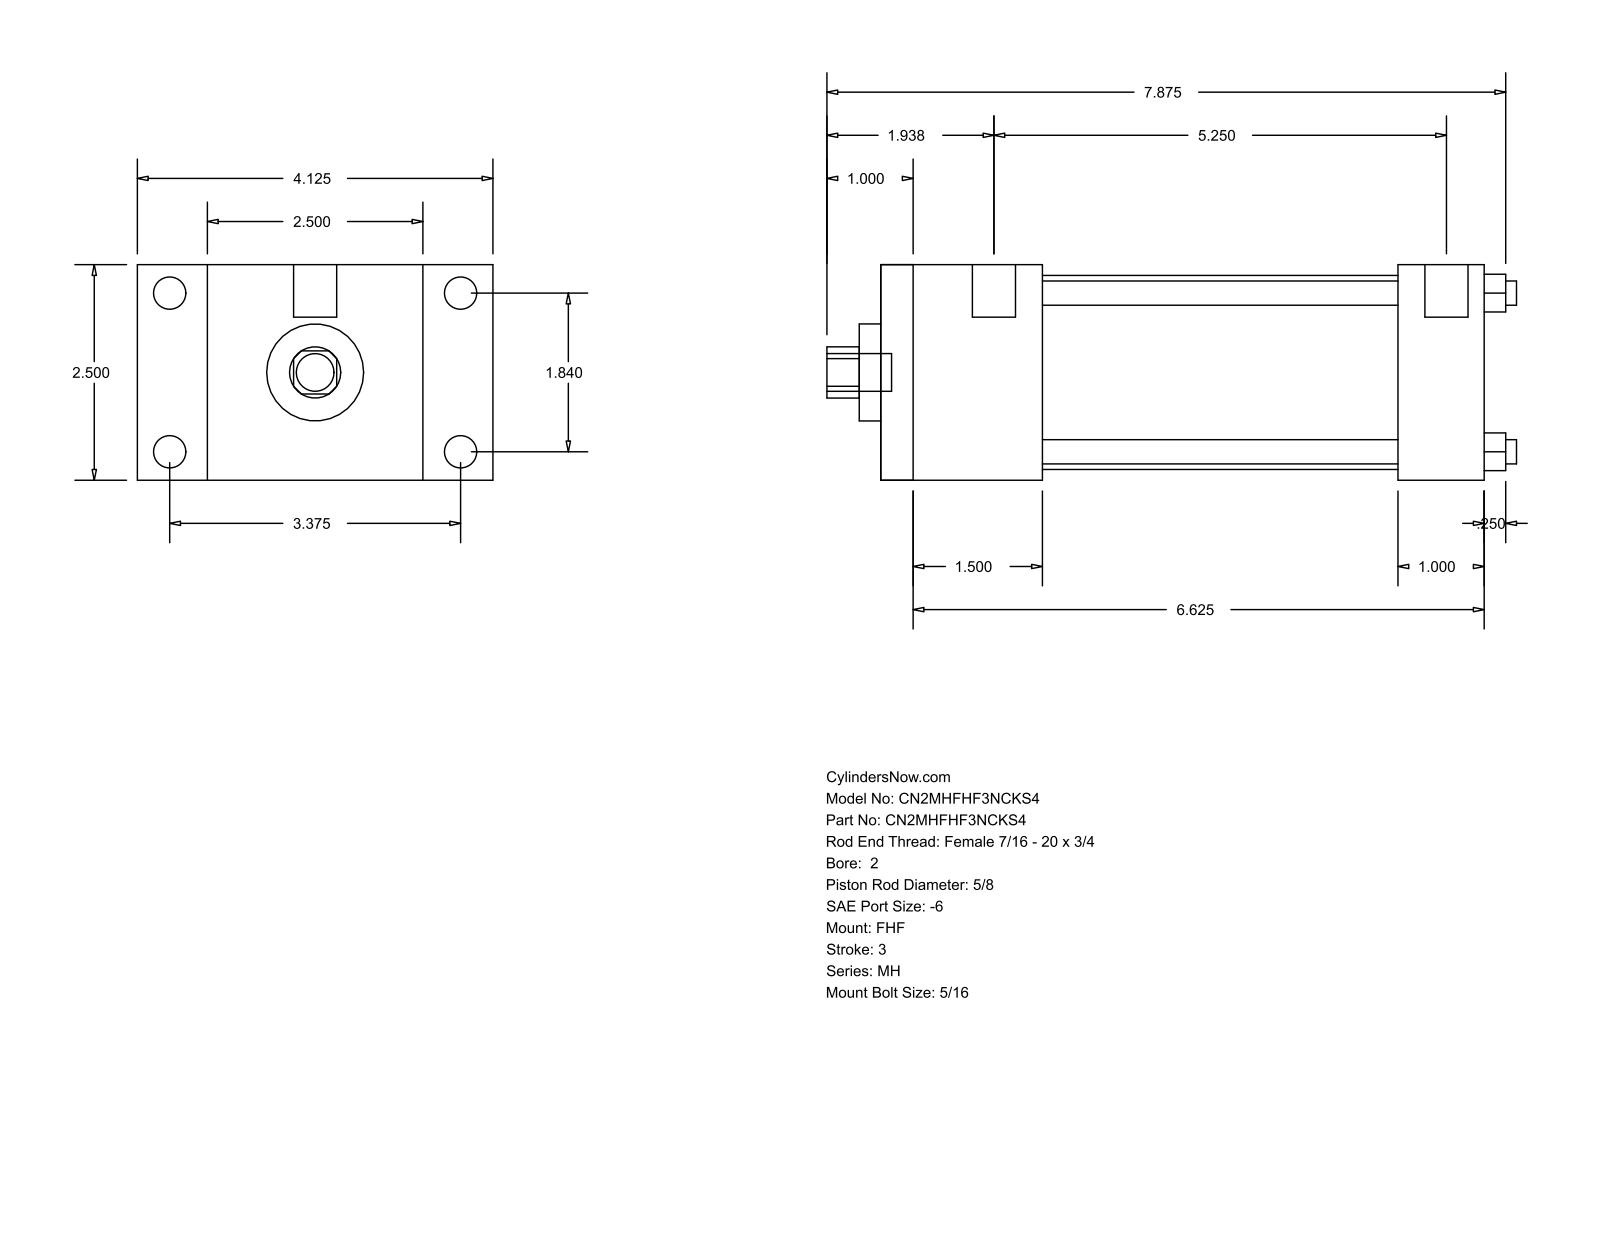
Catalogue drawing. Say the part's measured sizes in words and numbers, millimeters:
The part is named "MH_FHF__0200_0.625". Its 3-D file was written by "GSSL Pune (CONFIG_CONTROL_DESIGN)". It is 0 solids with 88 faces: 60 planar, 28 cylindrical and 0 other. Overall it measures 203.2 by 104.78 by 63.5 millimeters. Round holes: 4 of diameter 7.14, 1 of diameter 15.88, 1 of diameter 28.57, 1 of diameter 57.15. Round bosses or shafts: 4 of diameter 9.53, 4 of diameter 5.56, 2 of diameter 12.7, 1 of diameter 11.11. Partial cylindrical surfaces (rounded edges, fillets, slot ends): 1 of radius 7.54. The main face-to-face distances are 63.5, 104.78, 47.62, 177.8, 130.18, 20.64, 84.14, 25.4, 152.4, 184.15. The hole center spacings are 33.05, 46.74, 66.1.
